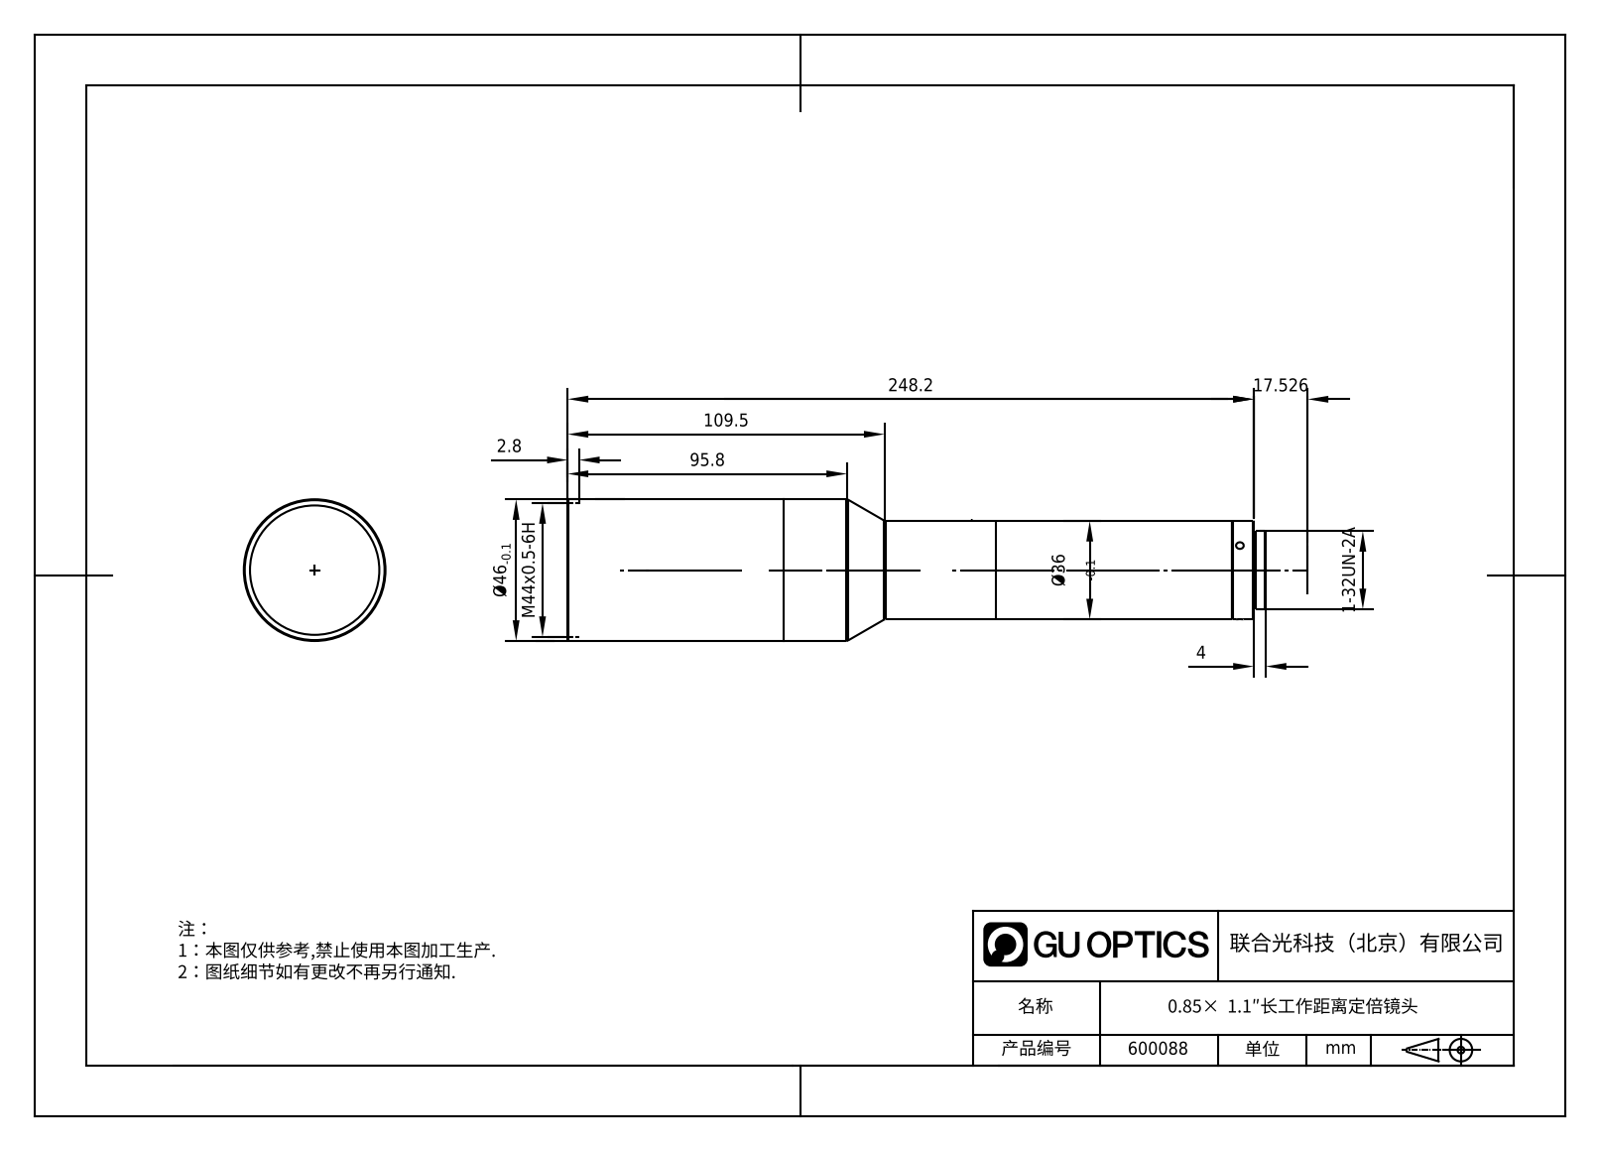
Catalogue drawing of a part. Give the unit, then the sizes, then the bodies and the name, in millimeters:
Units: millimetres
Overall size (bounding box): 252.19 × 46 × 46
Round holes (diameter × count): ⌀2.5 ×3, ⌀42 ×1, ⌀43.3 ×1
Round bosses / shafts (diameter × count): ⌀46 ×1, ⌀43 ×1, ⌀42.6 ×1, ⌀36 ×1, ⌀25.4 ×1, ⌀24.6 ×1
Partial cylindrical surfaces — rounded edges, fillets, slot ends (radius × count): R16.74 ×1
Main face-to-face distances: 239.19, 4, 243.19, 252.19, 248.19, 9, 0.8, 172.22, 175.42, 171.42
Volume: 314 507 mm³ · Surface area: 39 082 mm²
Bodies: 2 solids, 34 faces (10 planar, 15 cylindrical, 9 other)
Part name (STEP PRODUCT): 600088
STEP written by: SolidWorks 2020 (CONFIG_CONTROL_DESIGN)
